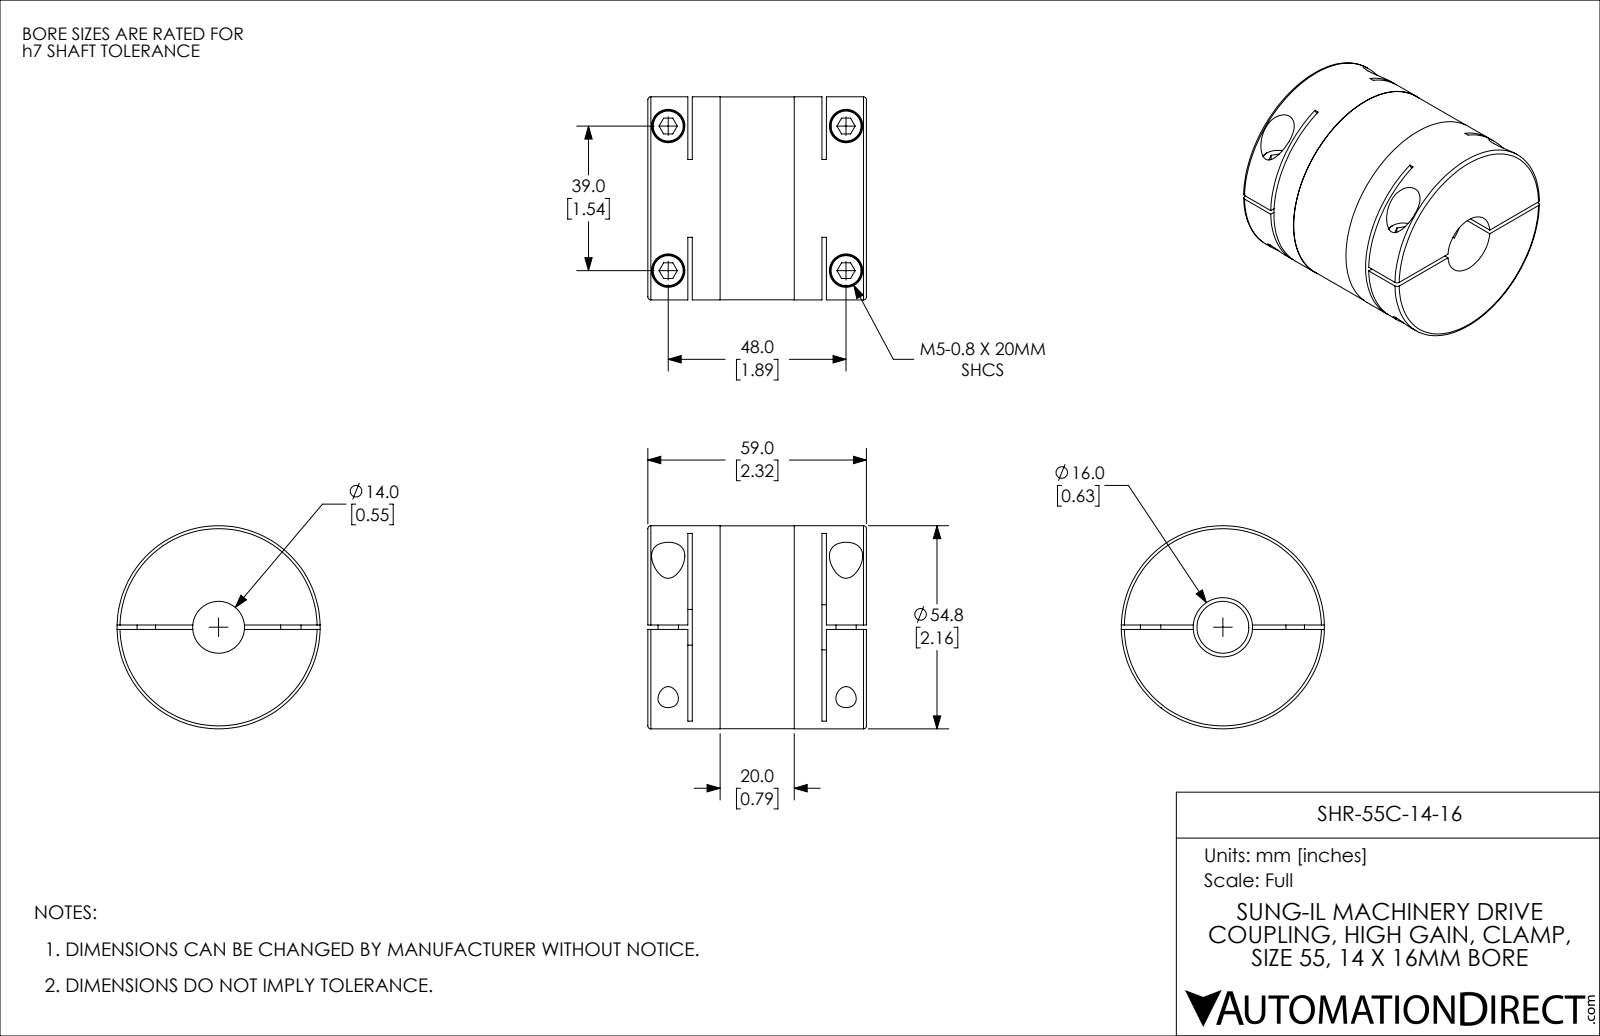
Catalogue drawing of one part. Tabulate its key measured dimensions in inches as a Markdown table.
| quantity | value |
| --- | --- |
| part name | SHR-55C-14-16 |
| STEP written by | SolidWorks 2021 (CONFIG_CONTROL_DESIGN) |
| units | inches |
| bodies | 1 solid, 144 faces (70 planar, 58 cylindrical, 16 other) |
| overall size | 2.323 × 2.157 × 2.157 |
| volume | 7.286 in³ |
| surface area | 44.14 in² |
| round holes (diameter × count) | 0.217 × 4, 0.354 × 4, 0.551 × 1, 0.63 × 1, 0.709 × 1 |
| round bosses / shafts (diameter × count) | 0.335 × 4, 0.197 × 2, 2.157 × 1, 2.154 × 1 |
| partial cylindrical surfaces (radius × count) | 2.362 × 2 |
| main face-to-face distances | 0.047, 0.472, 1.85, 0.425, 1.898, 1.425, 2.323, 1.378, 1.472, 0.768 |
| hole center spacings | 1.535, 1.89, 2.435 |
